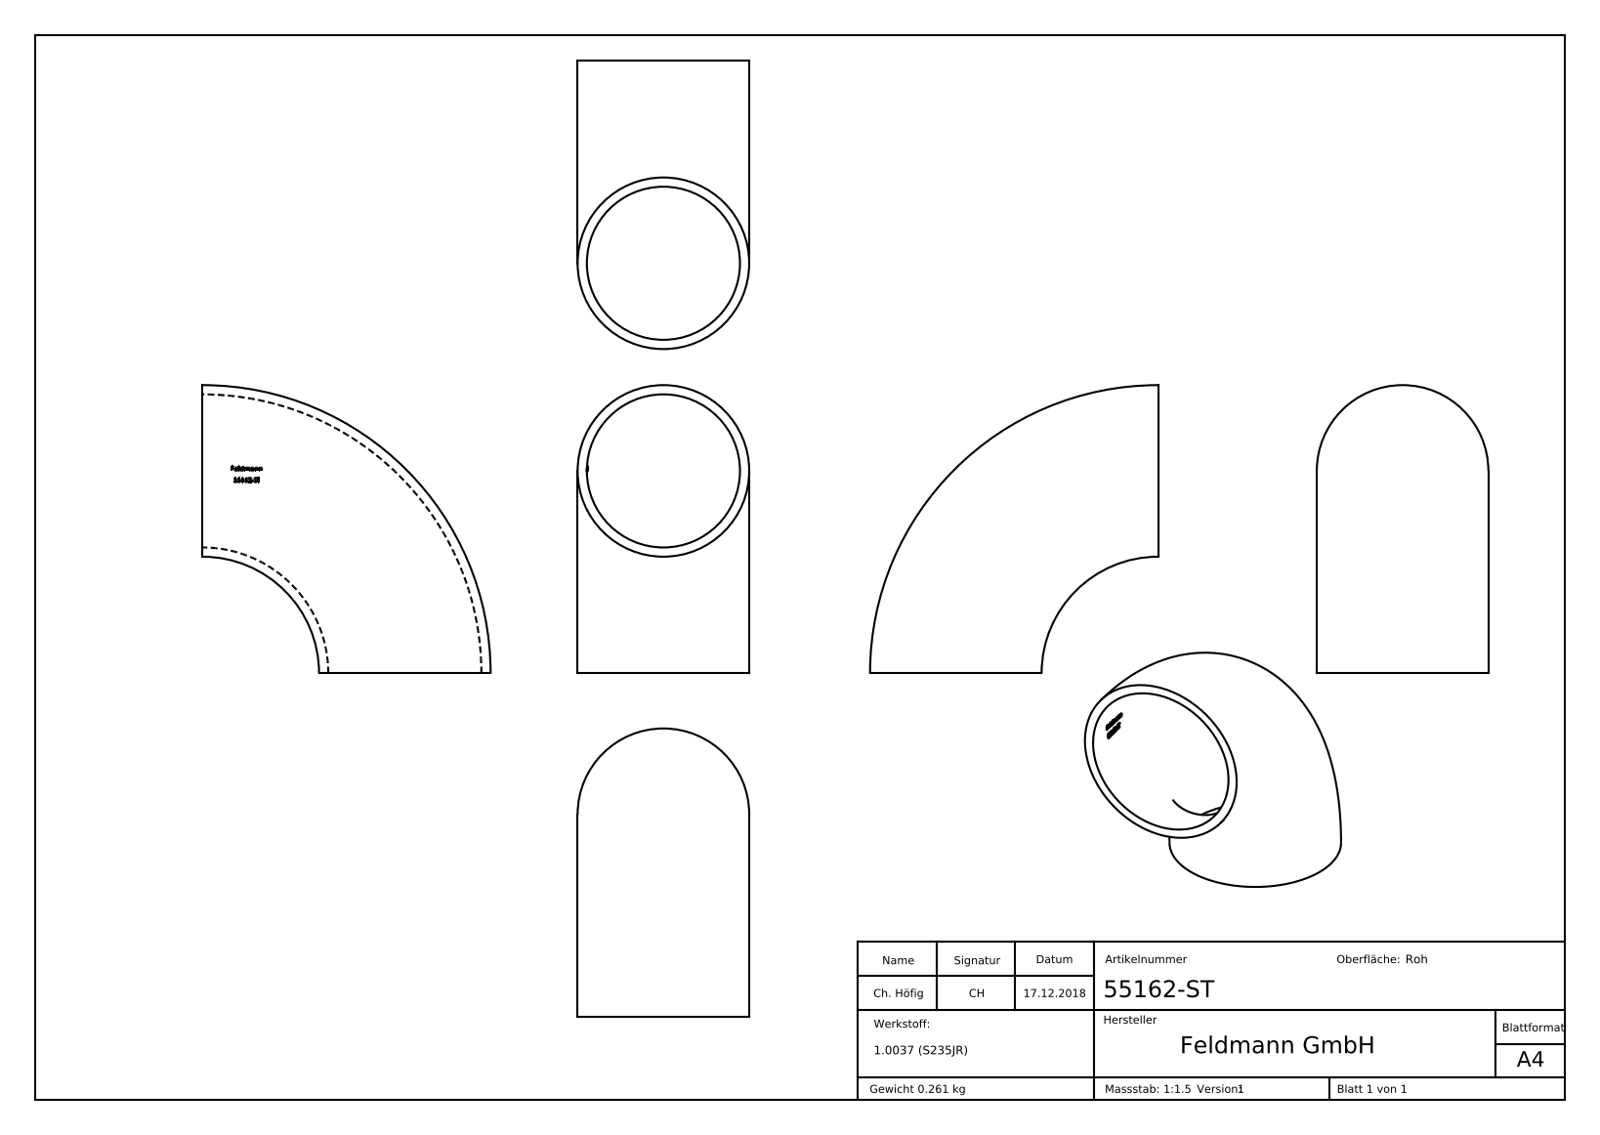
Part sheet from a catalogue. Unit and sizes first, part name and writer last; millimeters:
Units: millimetres
Overall size (bounding box): 81.15 × 81.15 × 48.3
Main face-to-face distances: 2.97, 3.09, 3.27, 3.54, 3.66, 1.32, 2.02, 4.43, 0.39, 1.19
Volume: 33 422 mm³ · Surface area: 26 464 mm²
Bodies: 1 solid, 215 faces (97 planar, 0 cylindrical, 118 other)
Part name (STEP PRODUCT): 55162-ST
STEP written by: SolidWorks 2015 (CONFIG_CONTROL_DESIGN)
